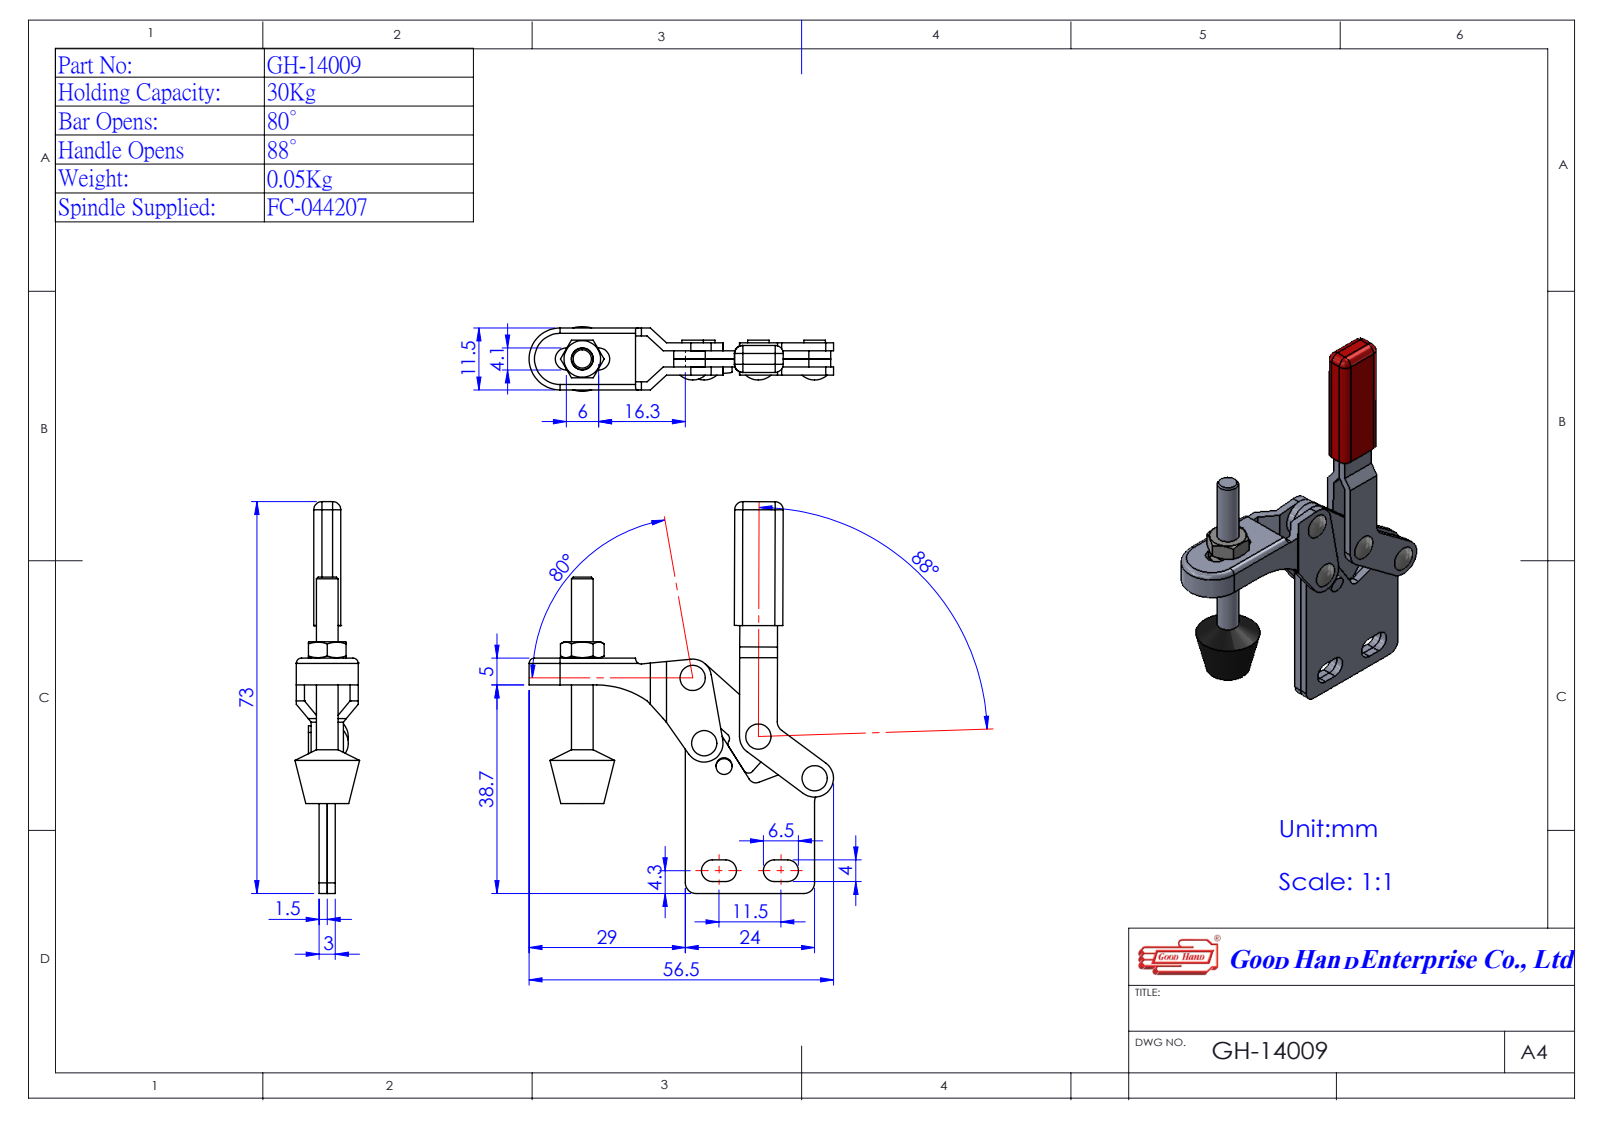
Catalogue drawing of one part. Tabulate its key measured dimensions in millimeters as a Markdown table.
| quantity | value |
| --- | --- |
| part name | GH-14009(簡化); Group5^GH-14009(簡化); Group2^GH-14009(簡化); Group3^GH-14009(簡化) (+2 more) |
| STEP written by | SolidWorks 2016 (AUTOMOTIVE_DESIGN) |
| units | millimeters |
| bodies | 5 solids, 219 faces (105 planar, 90 cylindrical, 24 other) |
| overall size | 72.72 × 56.5 × 12 |
| volume | 6 572 mm³ |
| surface area | 6 992 mm² |
| round holes (diameter × count) | 2.5 × 4 |
| round bosses / shafts (diameter × count) | 4 × 5, 7 × 1, 2.5 × 1 |
| partial cylindrical surfaces (radius × count) | 2 × 7, 1 × 4, 3.5 × 3, 1.5 × 2, 2.05 × 2, 3 × 1, 4.25 × 1, 5.75 × 1 |
| main face-to-face distances | 3, 1.5, 4.5, 0.5, 1, 4, 5.5, 6, 5, 2.75 |
| hole center spacings | 10.12, 12.26, 13, 16.19, 21.51, 29.15 |
